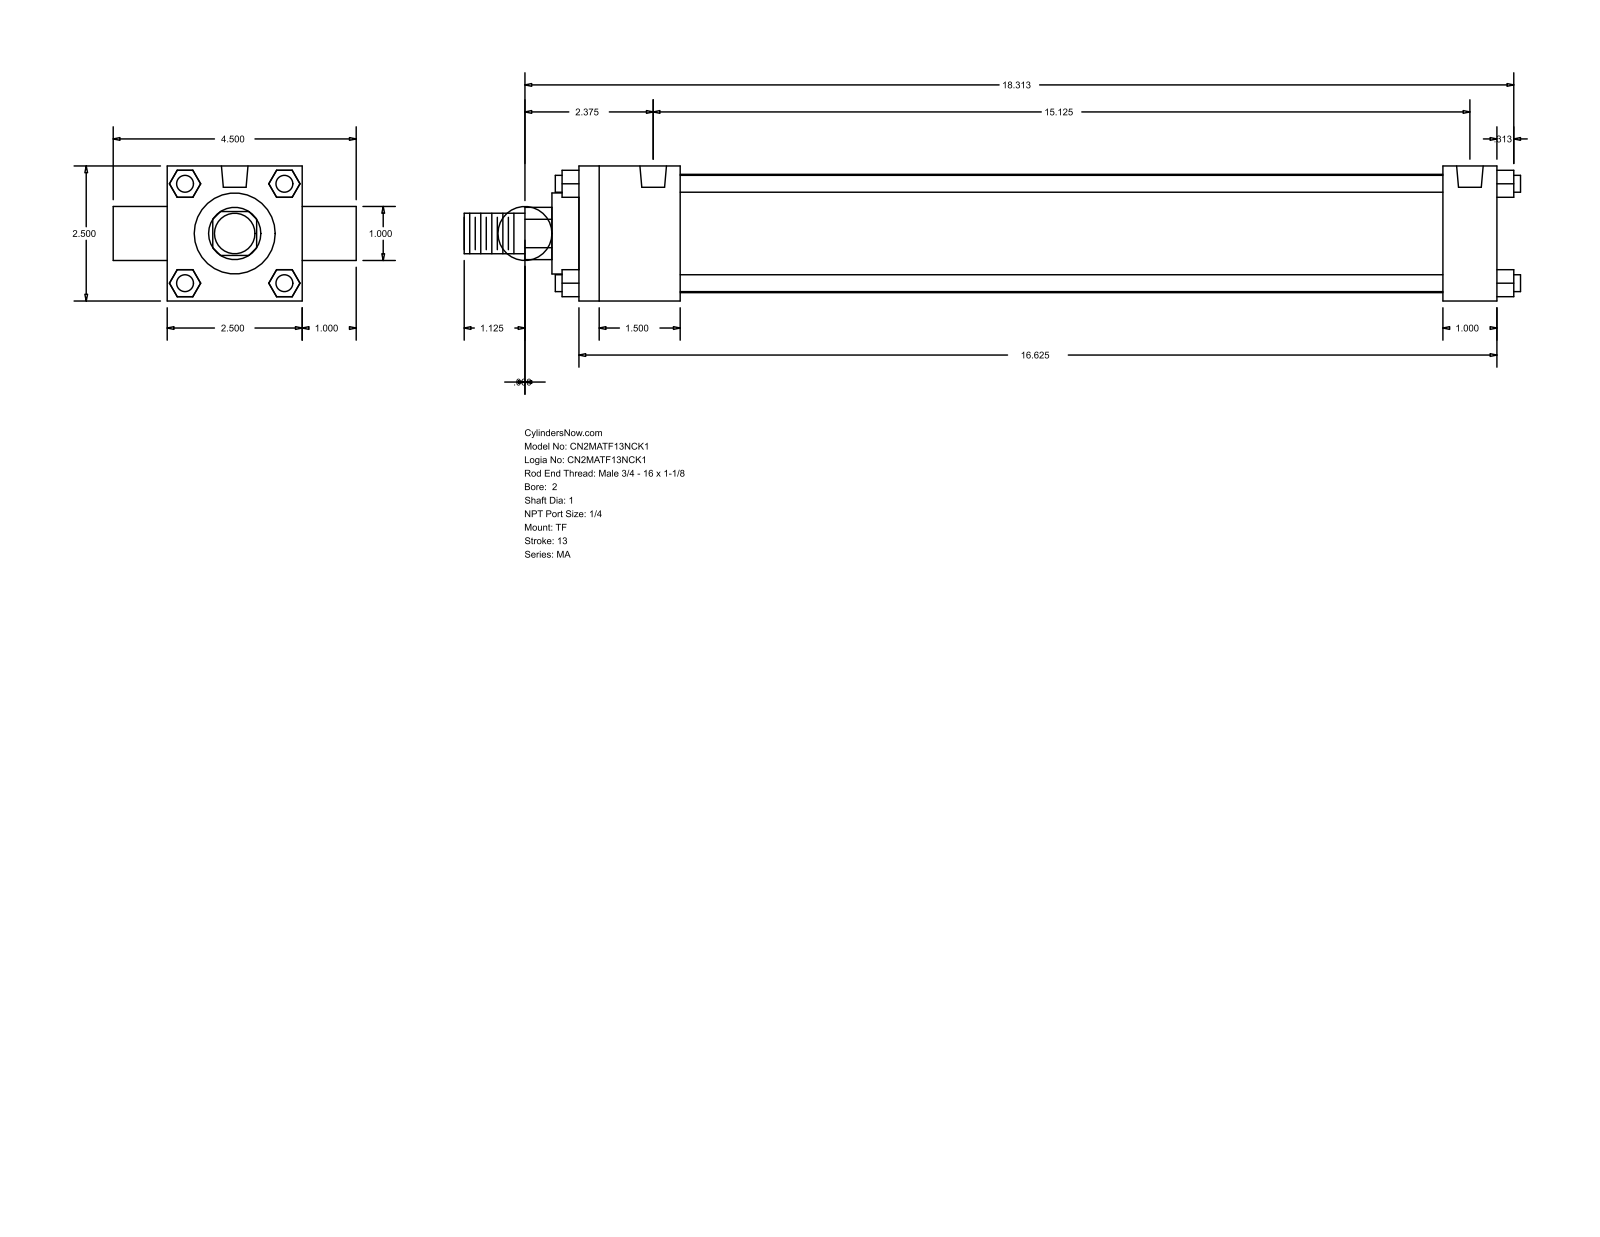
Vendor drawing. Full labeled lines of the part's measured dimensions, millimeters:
Part name (STEP PRODUCT): MA_TF__0200_1
STEP written by: GSSL Pune (CONFIG_CONTROL_DESIGN)
Units: millimetres
Bodies: 0 solids, 120 faces (92 planar, 28 cylindrical, 0 other)
Overall size (bounding box): 496.89 × 114.3 × 63.5
Round holes (diameter × count): ⌀7.94 ×3, ⌀12.49 ×2
Round bosses / shafts (diameter × count): ⌀7.94 ×4, ⌀25.4 ×2, ⌀55.63 ×1, ⌀38.1 ×1, ⌀19.05 ×1
Partial cylindrical surfaces — rounded edges, fillets, slot ends (radius × count): R12.29 ×1
Main face-to-face distances: 63.5, 25.4, 431.8, 12.7, 47.63, 406.4, 358.77, 384.17, 88.9, 23.37
Hole centre spacings: 384.17
